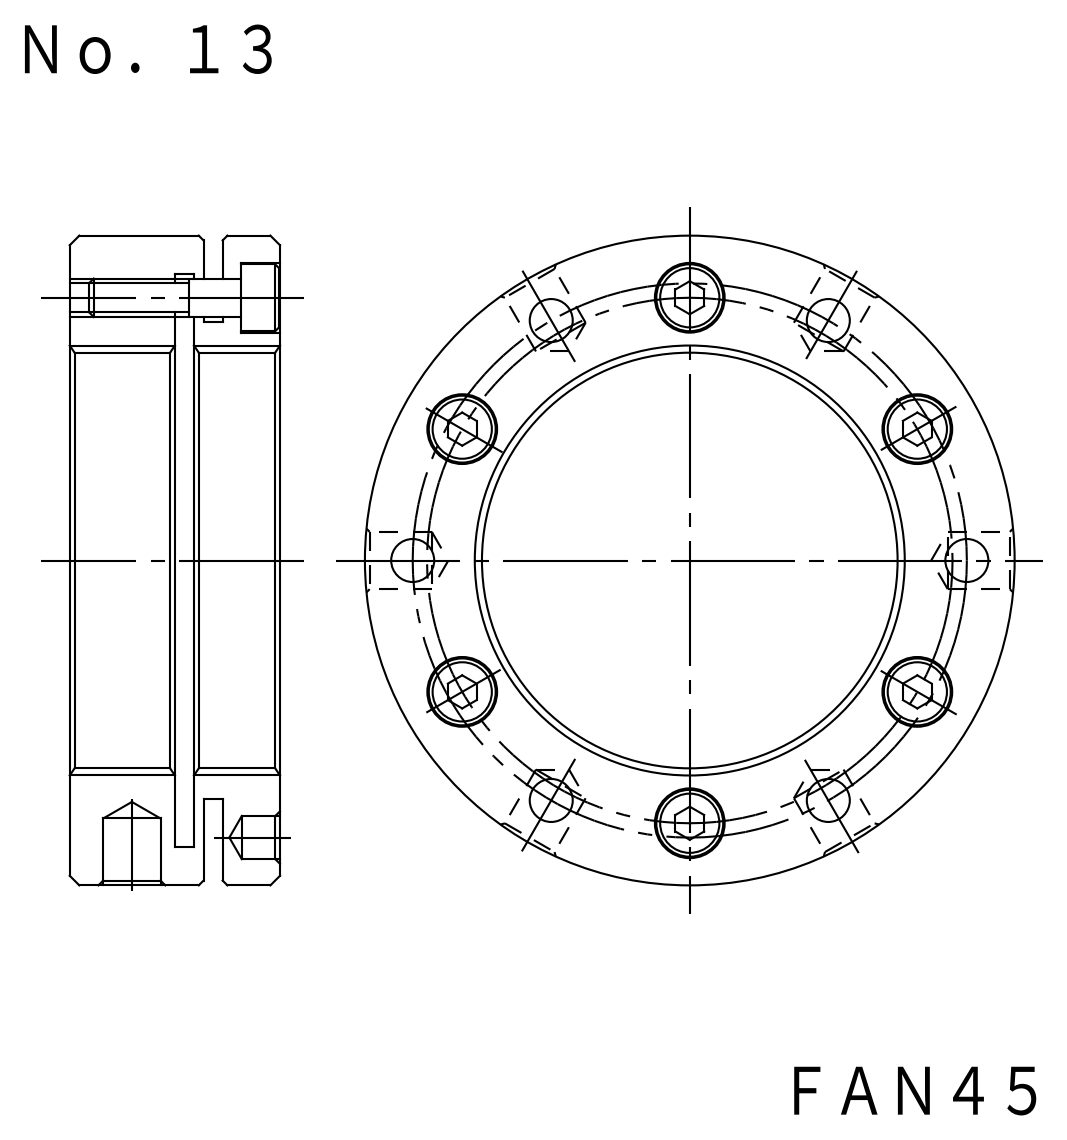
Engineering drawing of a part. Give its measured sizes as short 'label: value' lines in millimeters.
name: FKD FAN45; M4X16_default
written by: SolidWorks 2012 (CONFIG_CONTROL_DESIGN)
unit: mm
bodies: 7 solids, 204 faces (72 planar, 108 cylindrical, 24 other)
size: 68 × 68 × 22
volume: 37 550 mm³; area: 22 245 mm²
holes: 6× ⌀3.24, 6× ⌀4.3, 6× ⌀4.5, 6× ⌀7.3, 3× ⌀6, 1× ⌀45, 1× ⌀62
bosses: 6× ⌀7, 6× ⌀4, 1× ⌀68, 1× ⌀52
face distances: 2, 3, 11, 22, 16, 14, 8, 6, 5, 13
hole spacings: 14.89, 28.5, 29, 40.66, 55.54, 49.36, 50.23, 57
